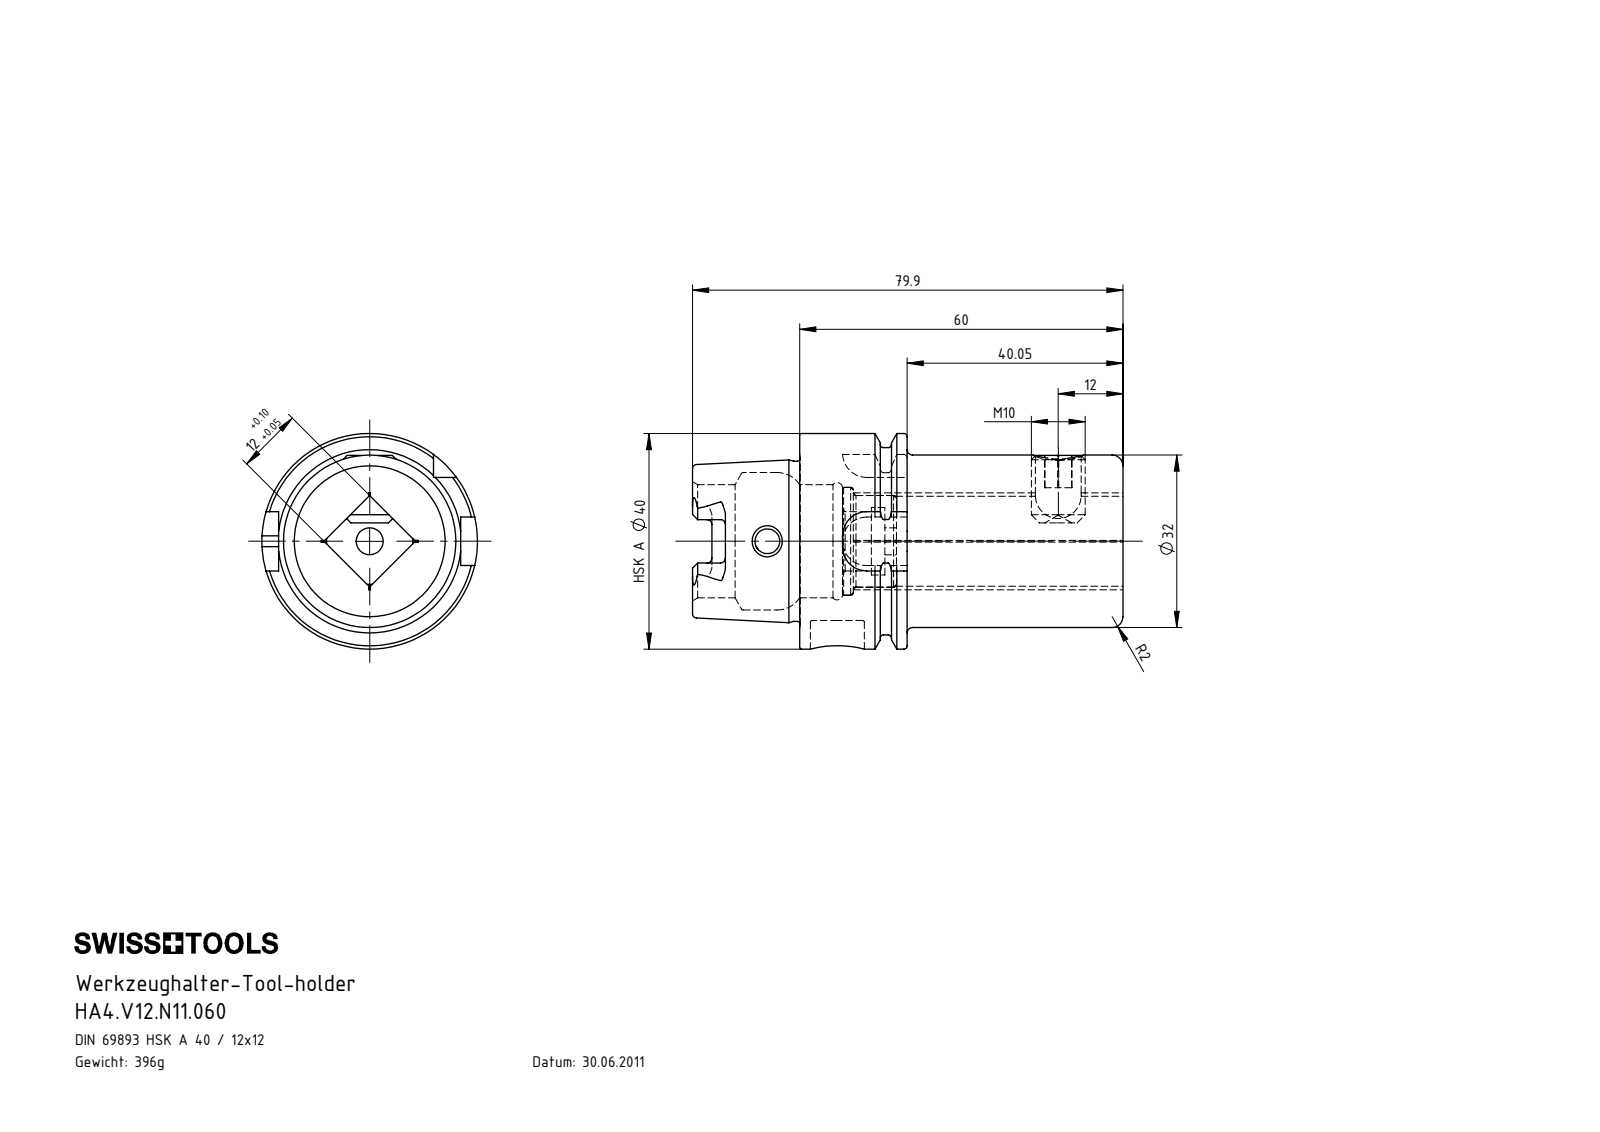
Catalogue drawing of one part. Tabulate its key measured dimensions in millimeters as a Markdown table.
| quantity | value |
| --- | --- |
| part name | W10-ER1.001.012; HA4-V12.N11.060_A_erodiert; Einsatz-HA4-V10-V12_Fertigbearbeitung; HA4.V12.N11.060 |
| STEP written by | SolidWorks 2022 (CONFIG_CONTROL_DESIGN) |
| units | millimeters |
| bodies | 3 solids, 230 faces (81 planar, 60 cylindrical, 89 other) |
| overall size | 79.9 × 40 × 40 |
| volume | 50 415 mm³ |
| surface area | 17 749 mm² |
| round holes (diameter × count) | 4.6 × 1, 5 × 1, 8.5 × 1, 10 × 1, 11 × 1, 12.5 × 1, 17 × 1, 20 × 1, 21 × 1, 25.5 × 1 |
| round bosses / shafts (diameter × count) | 40 × 1, 34.75 × 1, 32 × 1, 29.71 × 1, 10 × 1 |
| partial cylindrical surfaces (radius × count) | 0.9 × 6, 1.88 × 4, 4.5 × 4 |
| main face-to-face distances | 12, 60, 2, 10, 17.95, 42.05, 19.95, 40.05, 7.95, 52.05 |
| hole center spacings | 41 |
